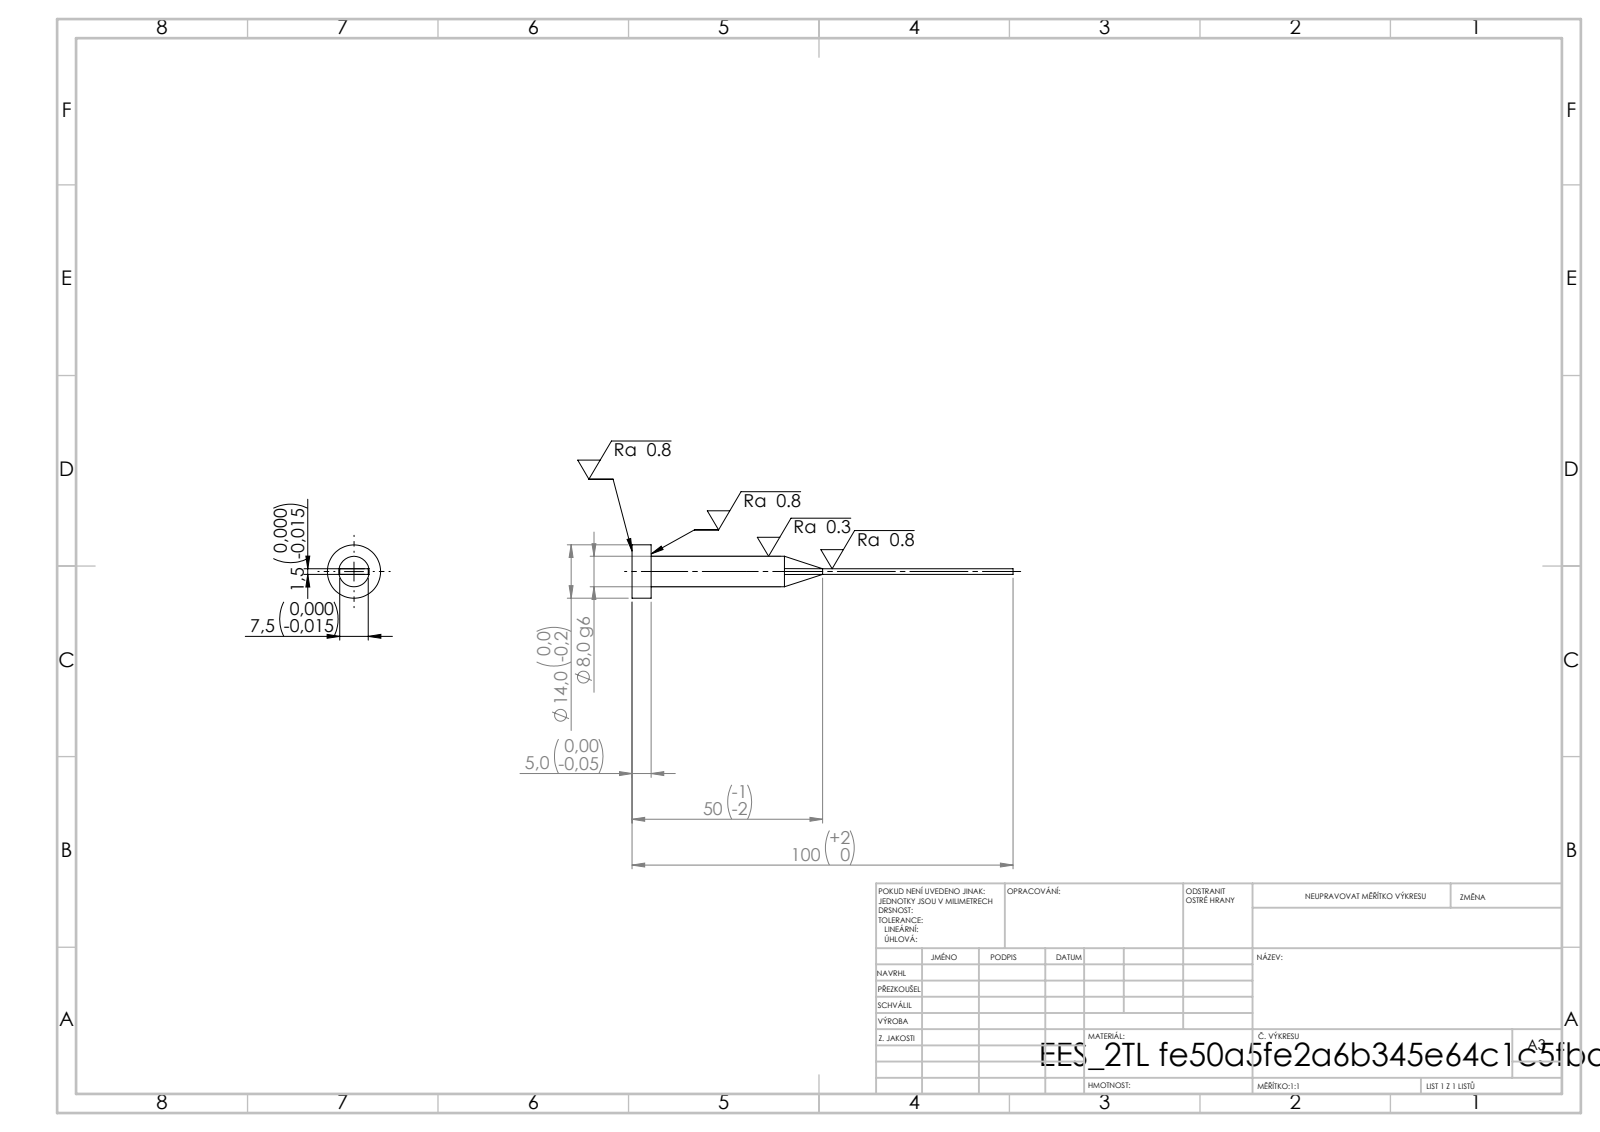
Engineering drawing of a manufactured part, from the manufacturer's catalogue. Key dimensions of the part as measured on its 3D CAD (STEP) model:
STEP written by: SolidWorks 2019 (CONFIG_CONTROL_DESIGN)
Units: millimetres
Bodies: 1 solid, 15 faces (7 planar, 4 cylindrical, 4 other)
Overall size (bounding box): 100 × 14 × 14
Volume: 3 384 mm³ · Surface area: 2 479 mm²
Round bosses / shafts (diameter × count): ⌀14 ×1, ⌀8 ×1
Main face-to-face distances: 1.5, 5, 7.5, 100, 95
